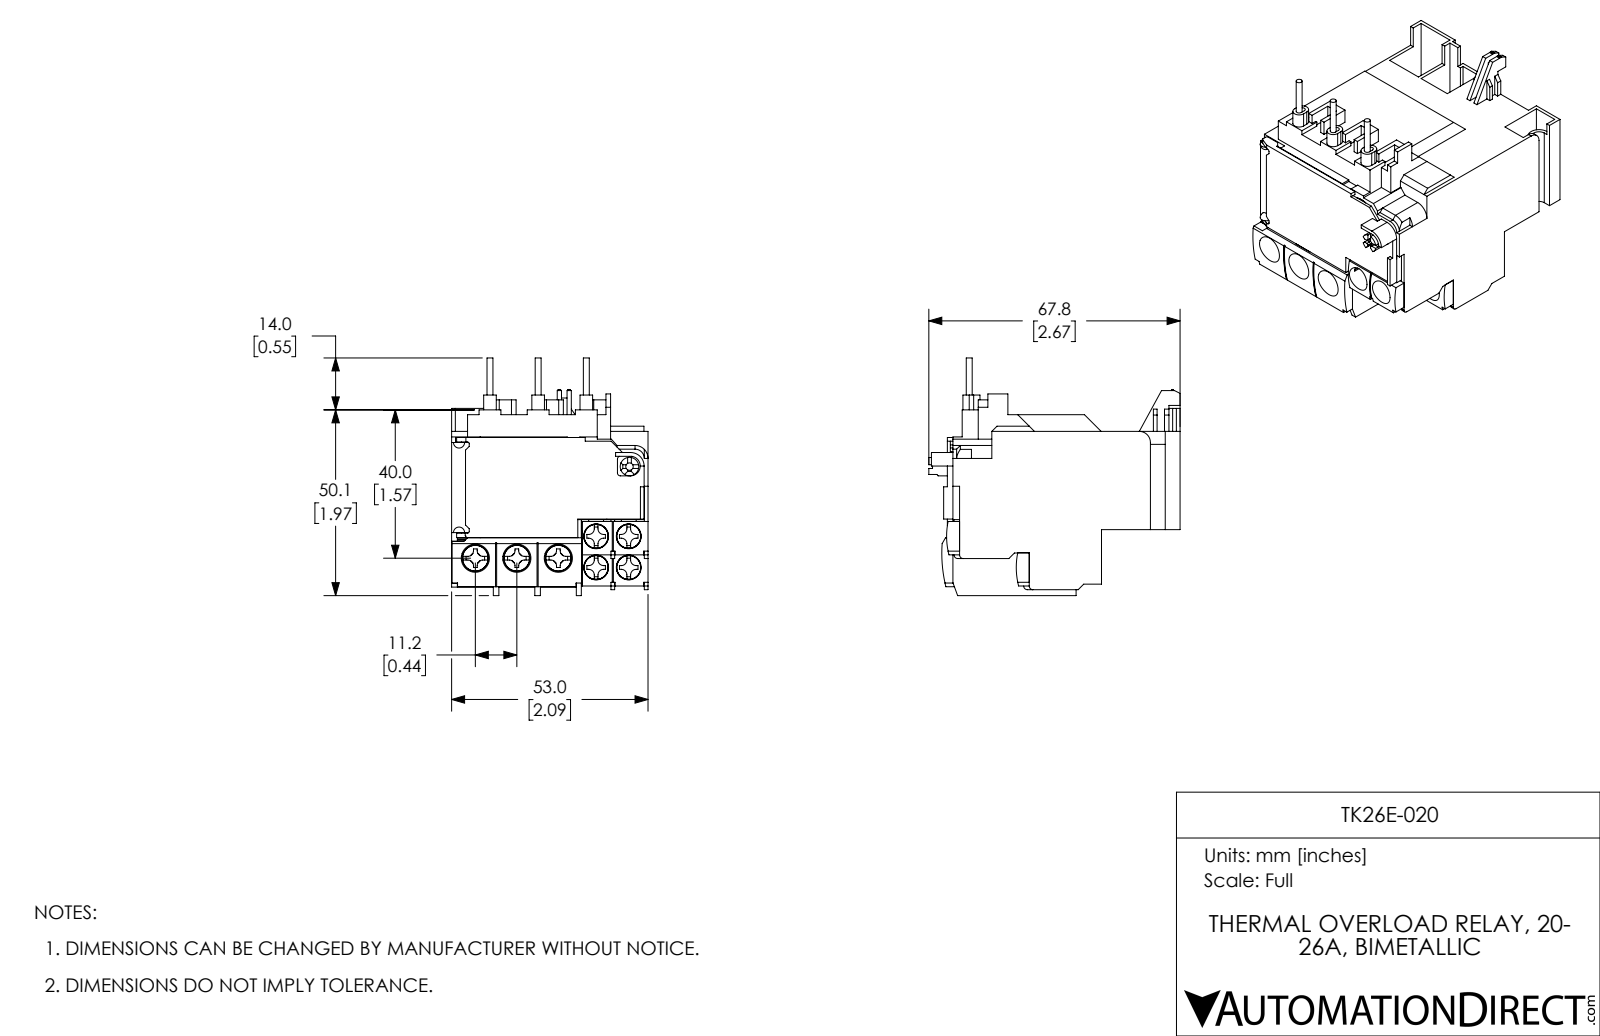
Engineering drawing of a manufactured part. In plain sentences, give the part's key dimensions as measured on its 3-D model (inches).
The part is named "TK26E-020". Its 3-D file was written by "SolidWorks 2017 (AUTOMOTIVE_DESIGN)". It is 38 solids with 1480 faces: 1225 planar, 220 cylindrical and 35 other. Overall it measures 2.669 by 2.524 by 2.087 inches. Its volume is 6.099 cubic inches and its surface area 60.15 square inches. Round holes: 4 of diameter 0.138, 4 of diameter 0.142, 4 of diameter 0.264, 3 of diameter 0.157, 3 of diameter 0.161, 3 of diameter 0.299, 1 of diameter 0.039, 1 of diameter 0.079, 1 of diameter 0.197, 1 of diameter 0.433. Round bosses or shafts: 4 of diameter 0.26, 3 of diameter 0.063, 1 of diameter 0.236. Partial cylindrical surfaces (rounded edges, fillets, slot ends): 28 of radius 0.059, 8 of radius 0.039, 6 of radius 0.02, 6 of radius 0.067, 5 of radius 0.031, 4 of radius 0.047, 4 of radius 0.171, 3 of radius 0.189. The main face-to-face distances are 0.039, 0.354, 0.059, 0.472, 2.087, 0.079, 0.394, 0.433, 0.343, 0.028. The hole center spacings are 0.331, 0.346, 0.441, 0.479, 0.376, 0.413, 0.464, 0.74.
